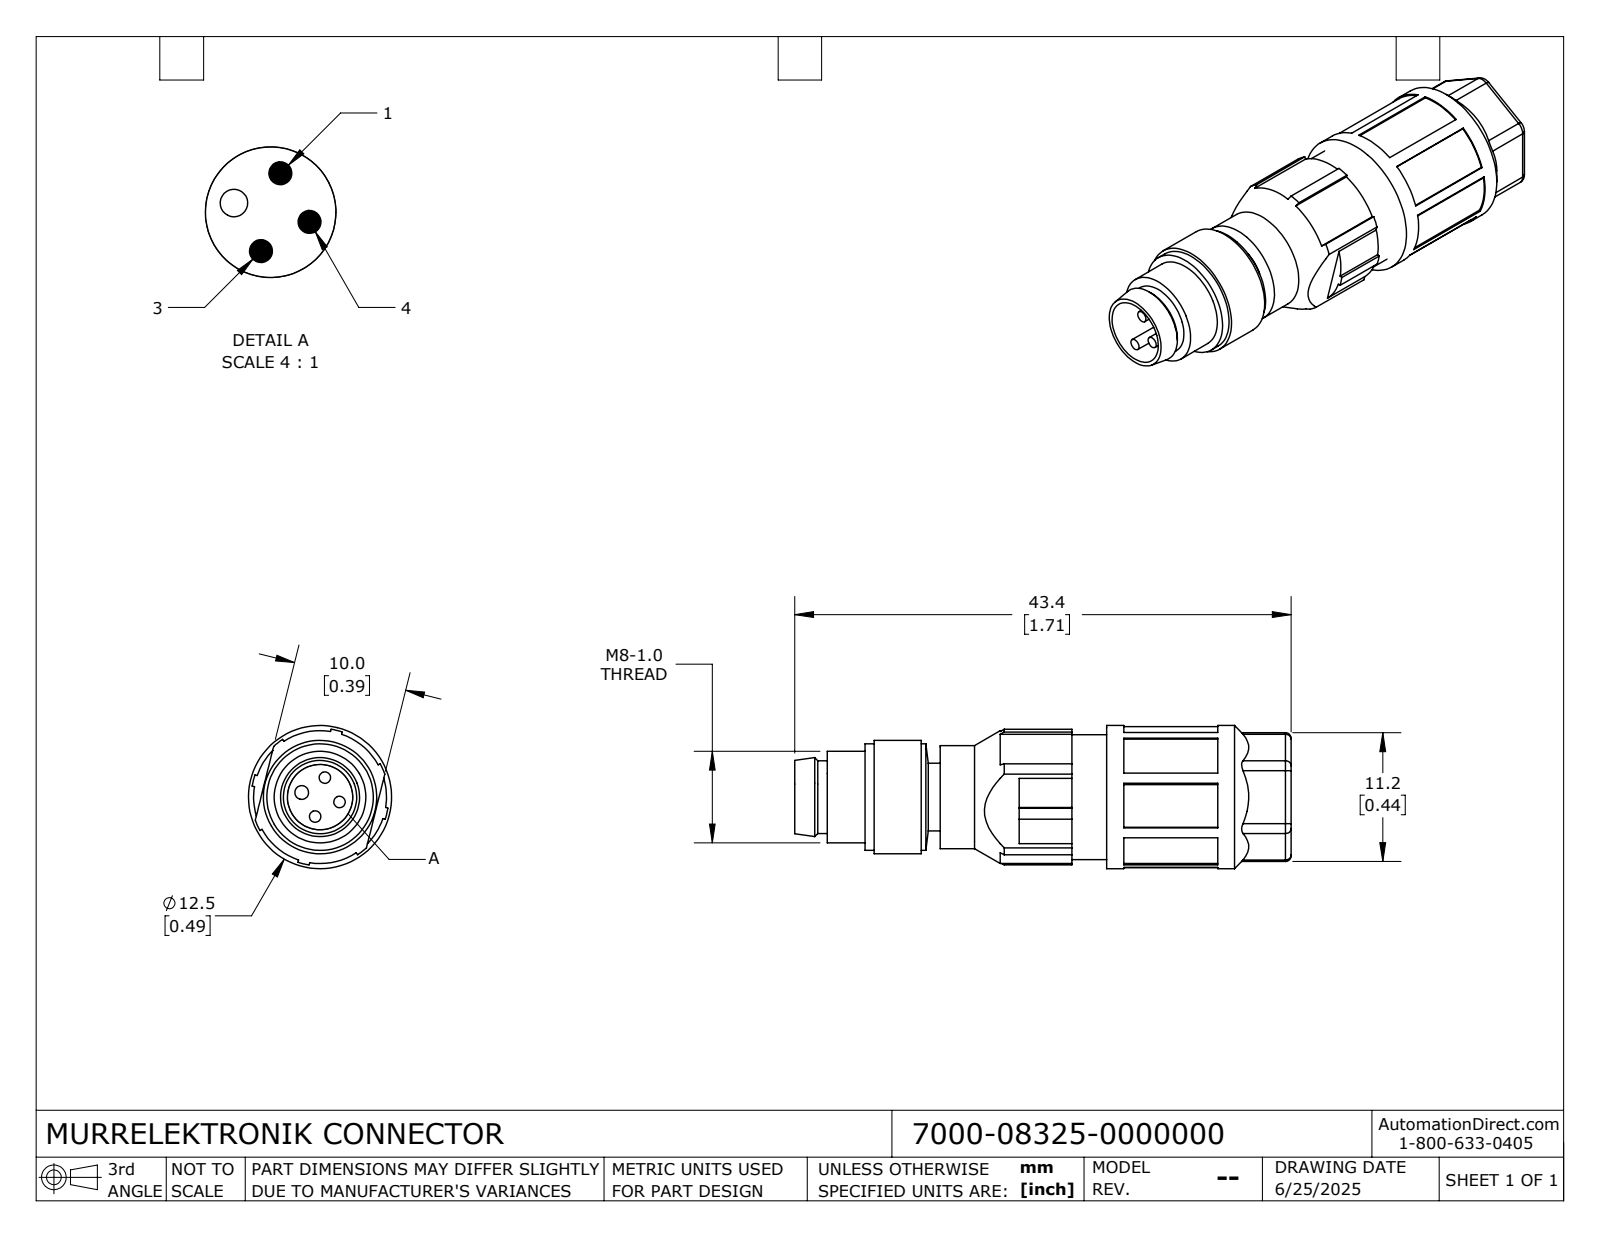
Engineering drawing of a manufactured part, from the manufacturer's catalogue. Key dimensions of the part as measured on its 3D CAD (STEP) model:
Part name (STEP PRODUCT): 7000-08325-0000000
STEP written by: SolidWorks 2024 (CONFIG_CONTROL_DESIGN)
Units: millimetres
Bodies: 2 solids, 413 faces (280 planar, 104 cylindrical, 29 other)
Overall size (bounding box): 43.35 × 12.5 × 12.5
Volume: 3 170 mm³ · Surface area: 4 009 mm²
Round holes (diameter × count): ⌀1.2 ×1, ⌀5.4 ×1, ⌀5.7 ×1, ⌀7 ×1, ⌀8.4 ×1, ⌀8.8 ×1, ⌀10 ×1
Round bosses / shafts (diameter × count): ⌀1 ×3, ⌀12.5 ×1, ⌀10.9 ×1, ⌀9.9 ×1, ⌀9.3 ×1, ⌀9 ×1, ⌀8.2 ×1, ⌀8 ×1
Partial cylindrical surfaces — rounded edges, fillets, slot ends (radius × count): R1 ×9, R0.8 ×8, R0.5 ×6, R5.8 ×1, R6 ×1, R6.15 ×1
Main face-to-face distances: 10, 0.37, 0.7, 5.54, 0.9, 0.8, 1.14, 1.07, 0.77, 1.4
Hole centre spacings: 1.65
